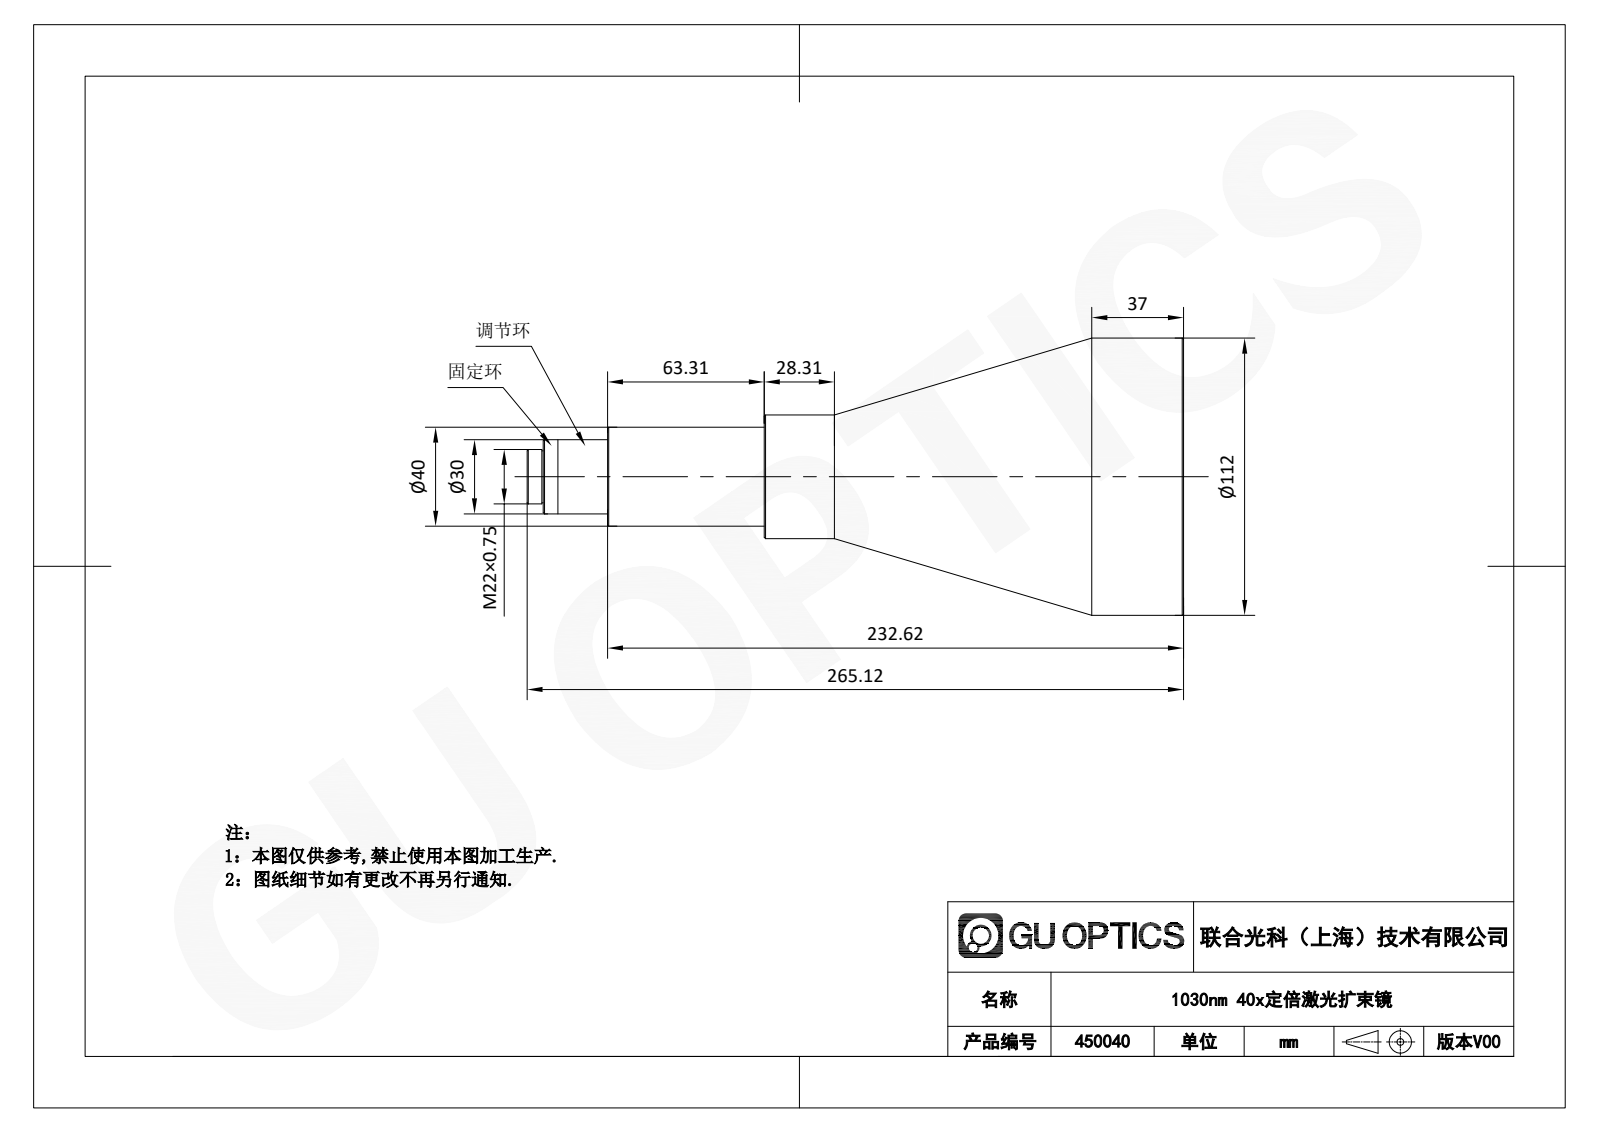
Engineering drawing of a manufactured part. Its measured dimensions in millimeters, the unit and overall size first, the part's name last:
Units: millimetres
Overall size (bounding box): 265.12 × 112 × 112
Round holes (diameter × count): ⌀8 ×1, ⌀100 ×1
Round bosses / shafts (diameter × count): ⌀112 ×1, ⌀50 ×1, ⌀40 ×1, ⌀30 ×1, ⌀22 ×1, ⌀21 ×1
Main face-to-face distances: 2, 167.31, 169.31, 63.31, 230.62, 232.62, 263.12, 26, 89.31, 256.62
Volume: 1 067 000 mm³ · Surface area: 68 261 mm²
Bodies: 1 solid, 36 faces (8 planar, 16 cylindrical, 12 other)
Part name (STEP PRODUCT): 450040
STEP written by: SolidWorks 2020 (CONFIG_CONTROL_DESIGN)
